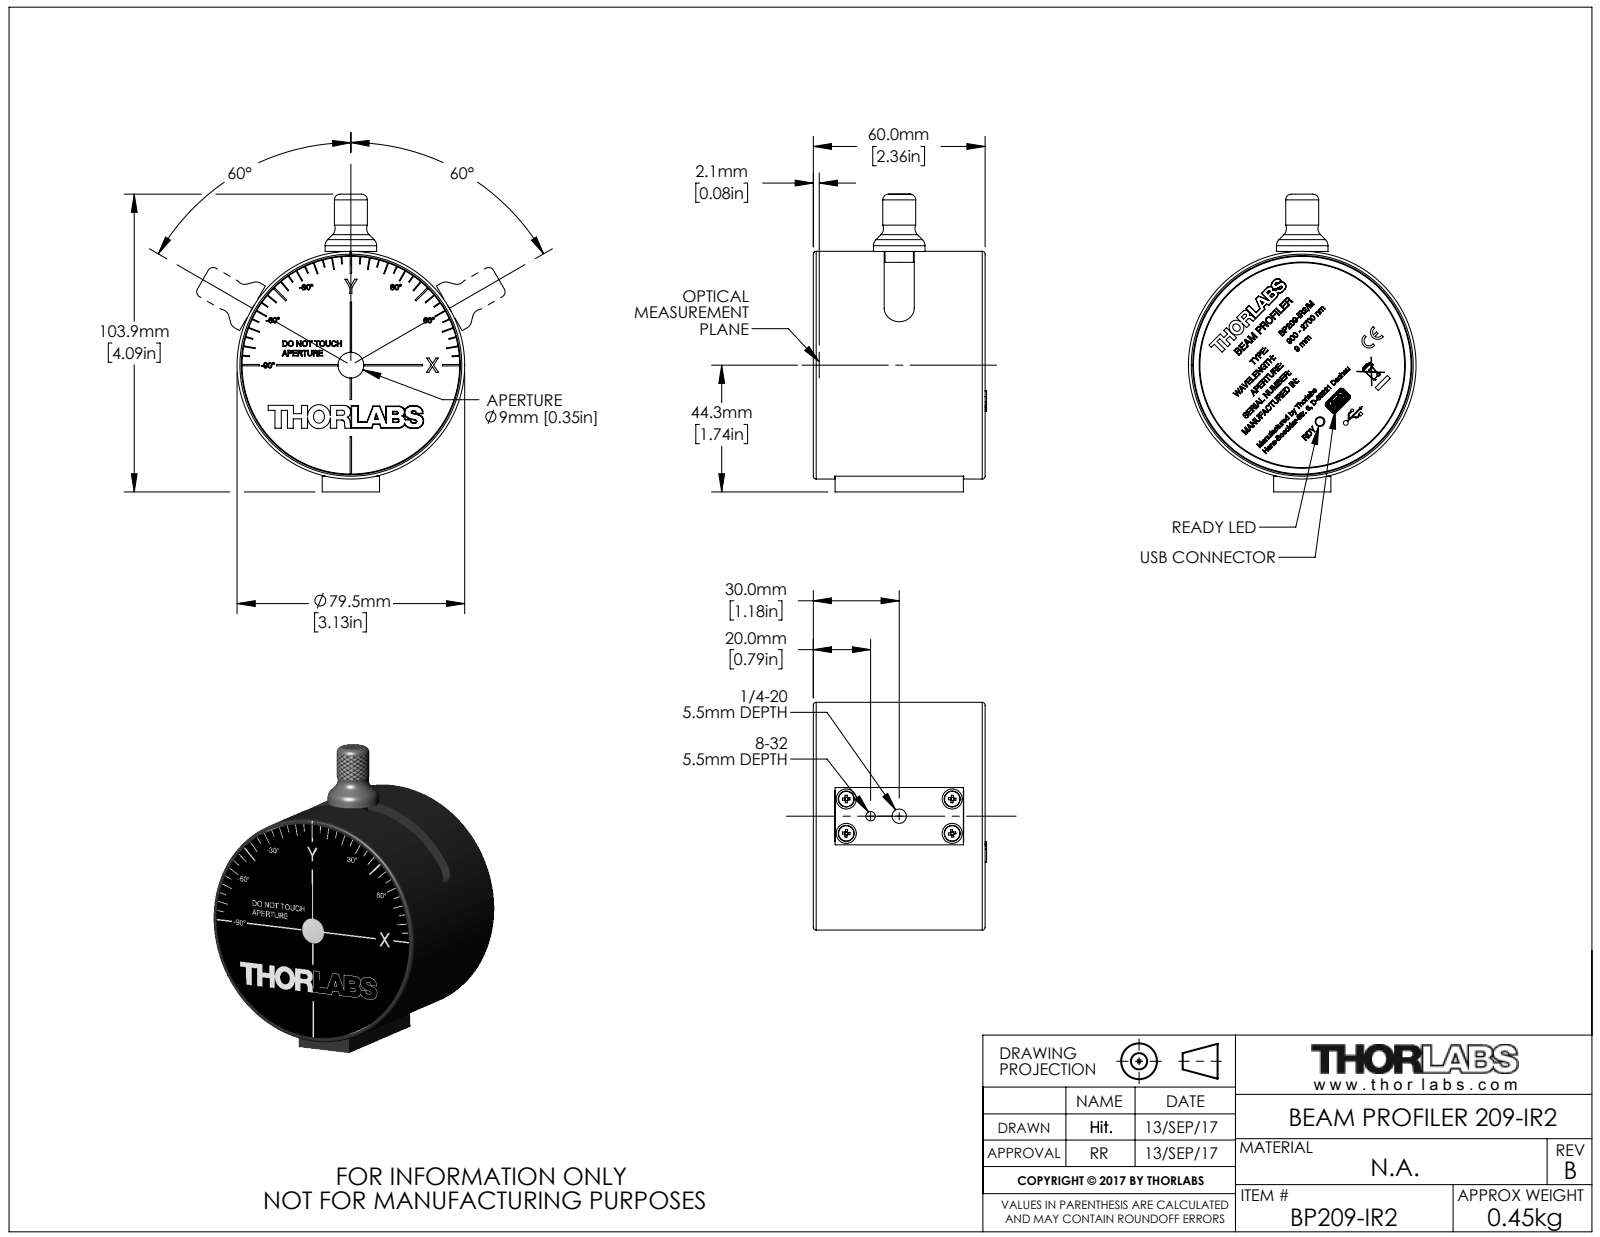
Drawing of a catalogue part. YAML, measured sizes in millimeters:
part_name: "MZN004188-E0W"
step_written_by: "SolidWorks 2016 (AUTOMOTIVE_DESIGN)"
units: millimeters
bodies: {solids: 14, faces: 4803, planar: 3242, cylindrical: 408, other: 1153}
overall_size: [103.95, 79.5, 60.5]
volume: 98412
surface_area: 99234
round_holes:
  - {diameter: 3.2, count: 10}
  - {diameter: 2.2, count: 9}
  - {diameter: 8, count: 8}
  - {diameter: 1.6, count: 6}
  - {diameter: 6.3, count: 6}
  - {diameter: 5, count: 5}
  - {diameter: 7, count: 5}
  - {diameter: 2.5, count: 4}
  - {diameter: 5.3, count: 4}
  - {diameter: 1, count: 1}
  - {diameter: 1.29, count: 1}
  - {diameter: 1.67, count: 1}
round_bosses_or_shafts:
  - {diameter: 5.6, count: 4}
  - {diameter: 3, count: 4}
  - {diameter: 0.8, count: 2}
  - {diameter: 79.5, count: 1}
  - {diameter: 76, count: 1}
  - {diameter: 72.1, count: 1}
  - {diameter: 71.8, count: 1}
  - {diameter: 71.5, count: 1}
partial_cylinders:
  - {radius: 1.5, count: 18}
  - {radius: 4, count: 16}
  - {radius: 0.1, count: 14}
  - {radius: 0.2, count: 14}
  - {radius: 1, count: 14}
  - {radius: 0.3, count: 9}
  - {radius: 0.7, count: 8}
  - {radius: 5, count: 8}
face_to_face_distances: [1, 59, 59.7, 60, 58, 0.7, 58.7, 0.5, 2, 1.5]
hole_center_spacings: [23.73, 31, 43.84, 57.28, 27, 46.77, 27.01, 19.45]
